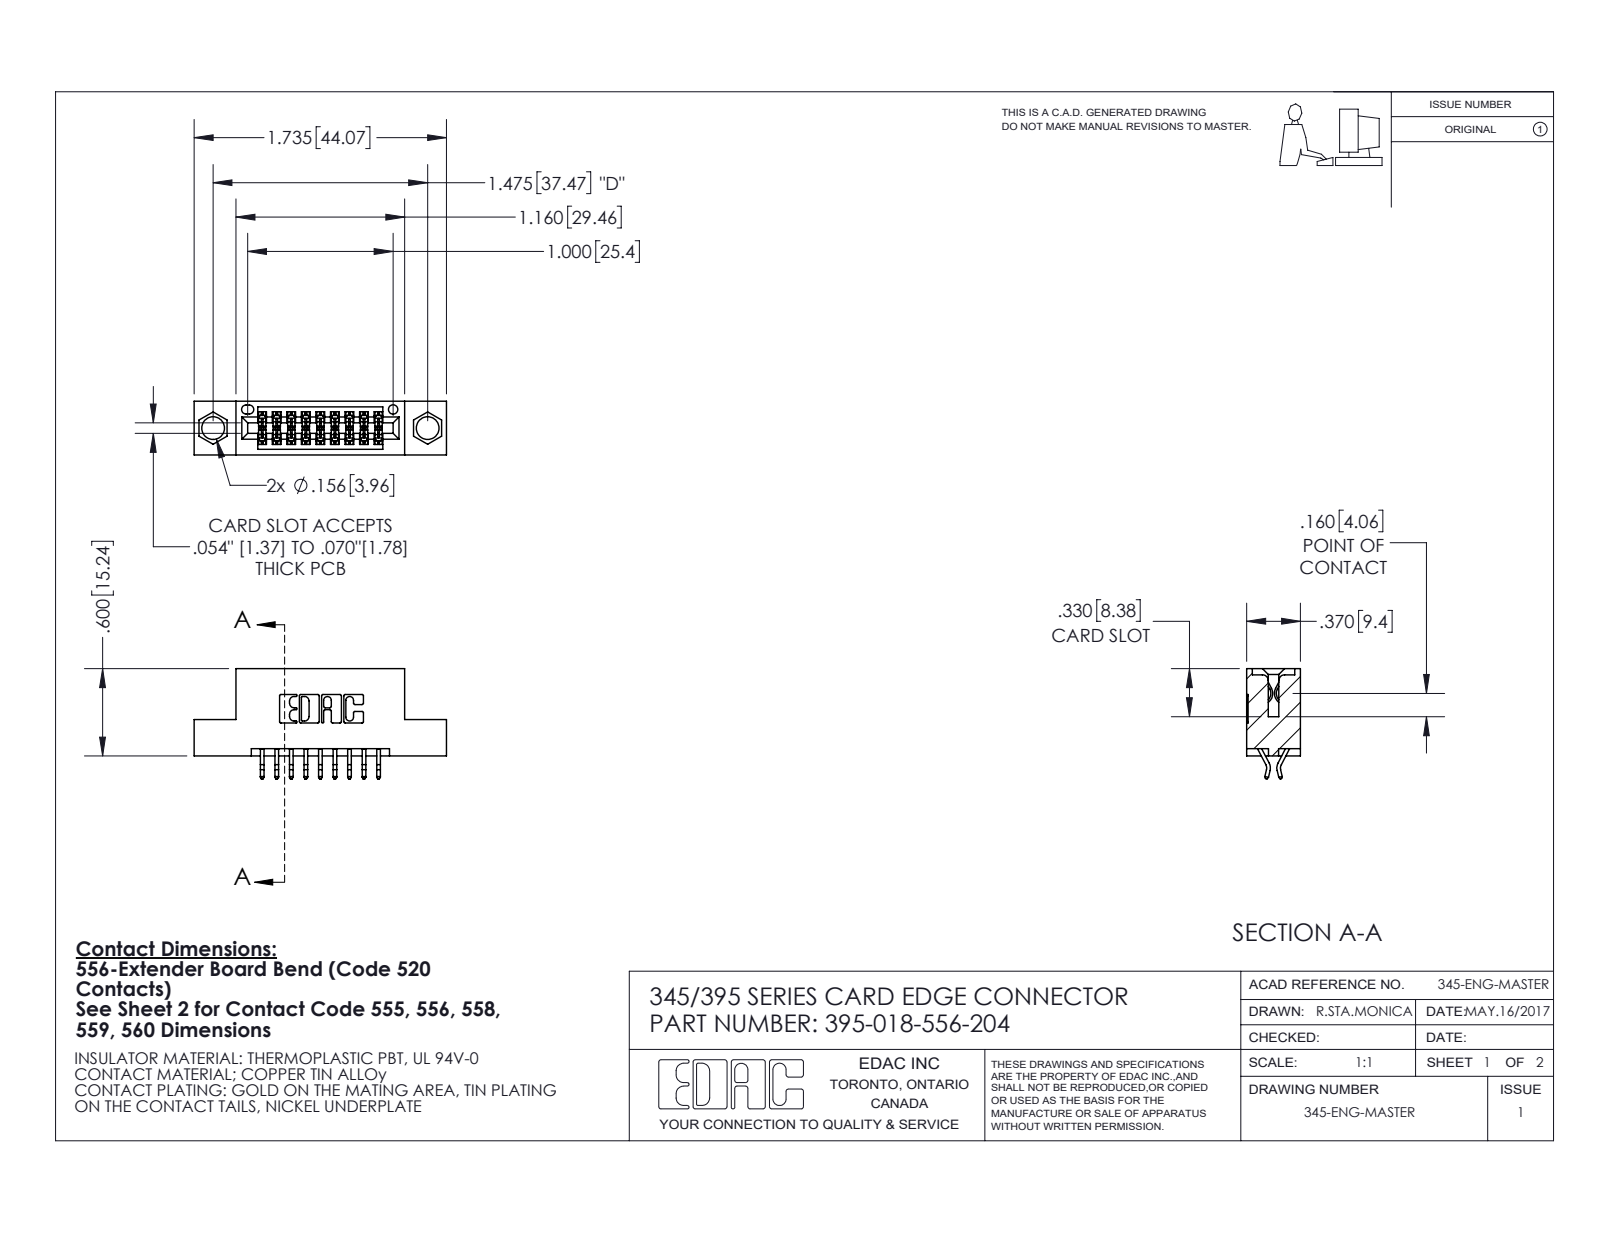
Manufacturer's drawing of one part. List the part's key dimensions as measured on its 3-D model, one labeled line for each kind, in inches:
Part name (STEP PRODUCT): 395-018-556-204; 345 Part_Flush Mounting Lugs - 0.156 Dia-TI; 345-292-001_556 Tail
STEP written by: SolidWorks 2020 (CONFIG_CONTROL_DESIGN)
Units: inches
Bodies: 19 solids, 1148 faces (760 planar, 388 cylindrical, 0 other)
Overall size (bounding box): 1.735 × 0.757 × 0.37
Volume: 0.236 in³ · Surface area: 7.617 in²
Round holes (diameter × count): ⌀0.156 ×2, ⌀0.064 ×1
Partial cylindrical surfaces — rounded edges, fillets, slot ends (radius × count): R0.006 ×36, R0.01 ×22, R0.007 ×6, R0.031 ×6, R0.026 ×3, R0.01 ×2, R0.014 ×2, R0.019 ×2
Main face-to-face distances: 0.2, 0.298, 0.072, 0.37, 0.1, 0.025, 0.098, 0.272, 0.6, 0.225
Hole centre spacings: 0.27, 1.244, 1.475
